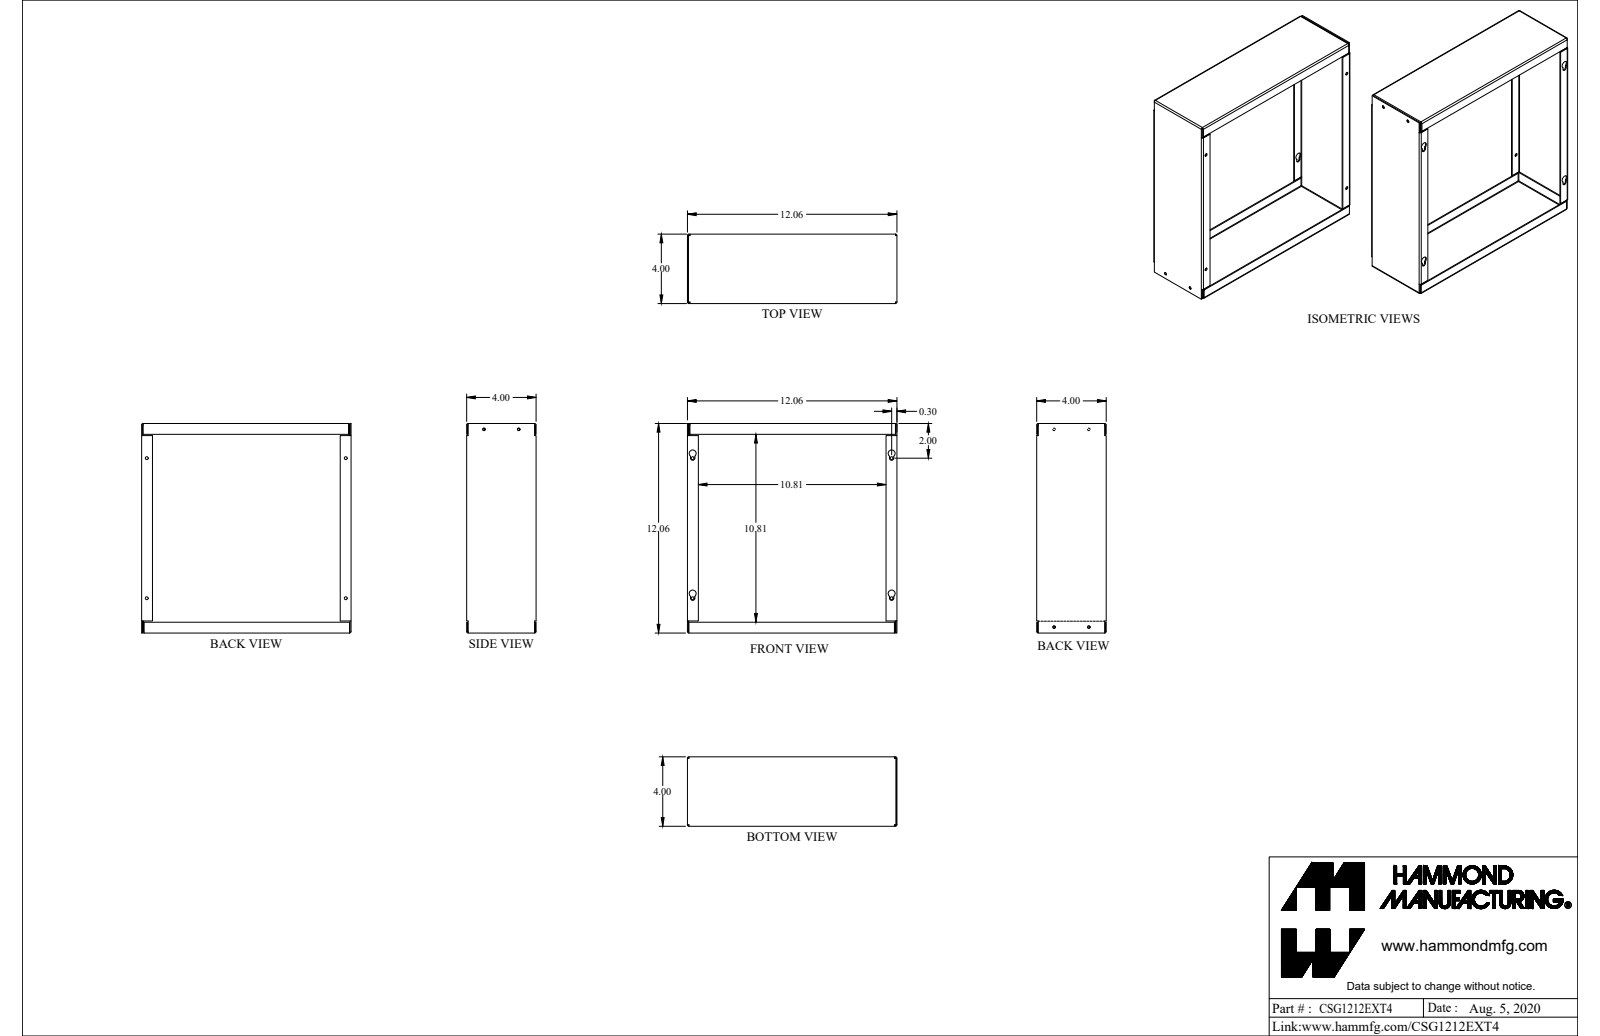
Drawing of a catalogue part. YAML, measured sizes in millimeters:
part_name: "CSG1212EXT4"
step_written_by: "SolidWorks 2021 (AUTOMOTIVE_DESIGN)"
units: millimeters
bodies: {solids: 2, faces: 124, planar: 80, cylindrical: 44, other: 0}
overall_size: [306.4, 306.4, 101.6]
volume: 227900
surface_area: 319900
round_holes:
  - {diameter: 3.7, count: 4}
  - {diameter: 4.3, count: 4}
round_bosses_or_shafts:
  - {diameter: 3.3, count: 4}
partial_cylinders:
  - {radius: 0.7, count: 12}
  - {radius: 2.2, count: 12}
  - {radius: 3.2, count: 4}
  - {radius: 5.2, count: 4}
face_to_face_distances: [305, 1.4, 1.4, 303.5, 100.2, 306.4, 306.4, 303.5, 98.7, 101.6]
hole_center_spacings: [50.8, 204.8, 289.1, 291.1, 293.5, 355.9]
